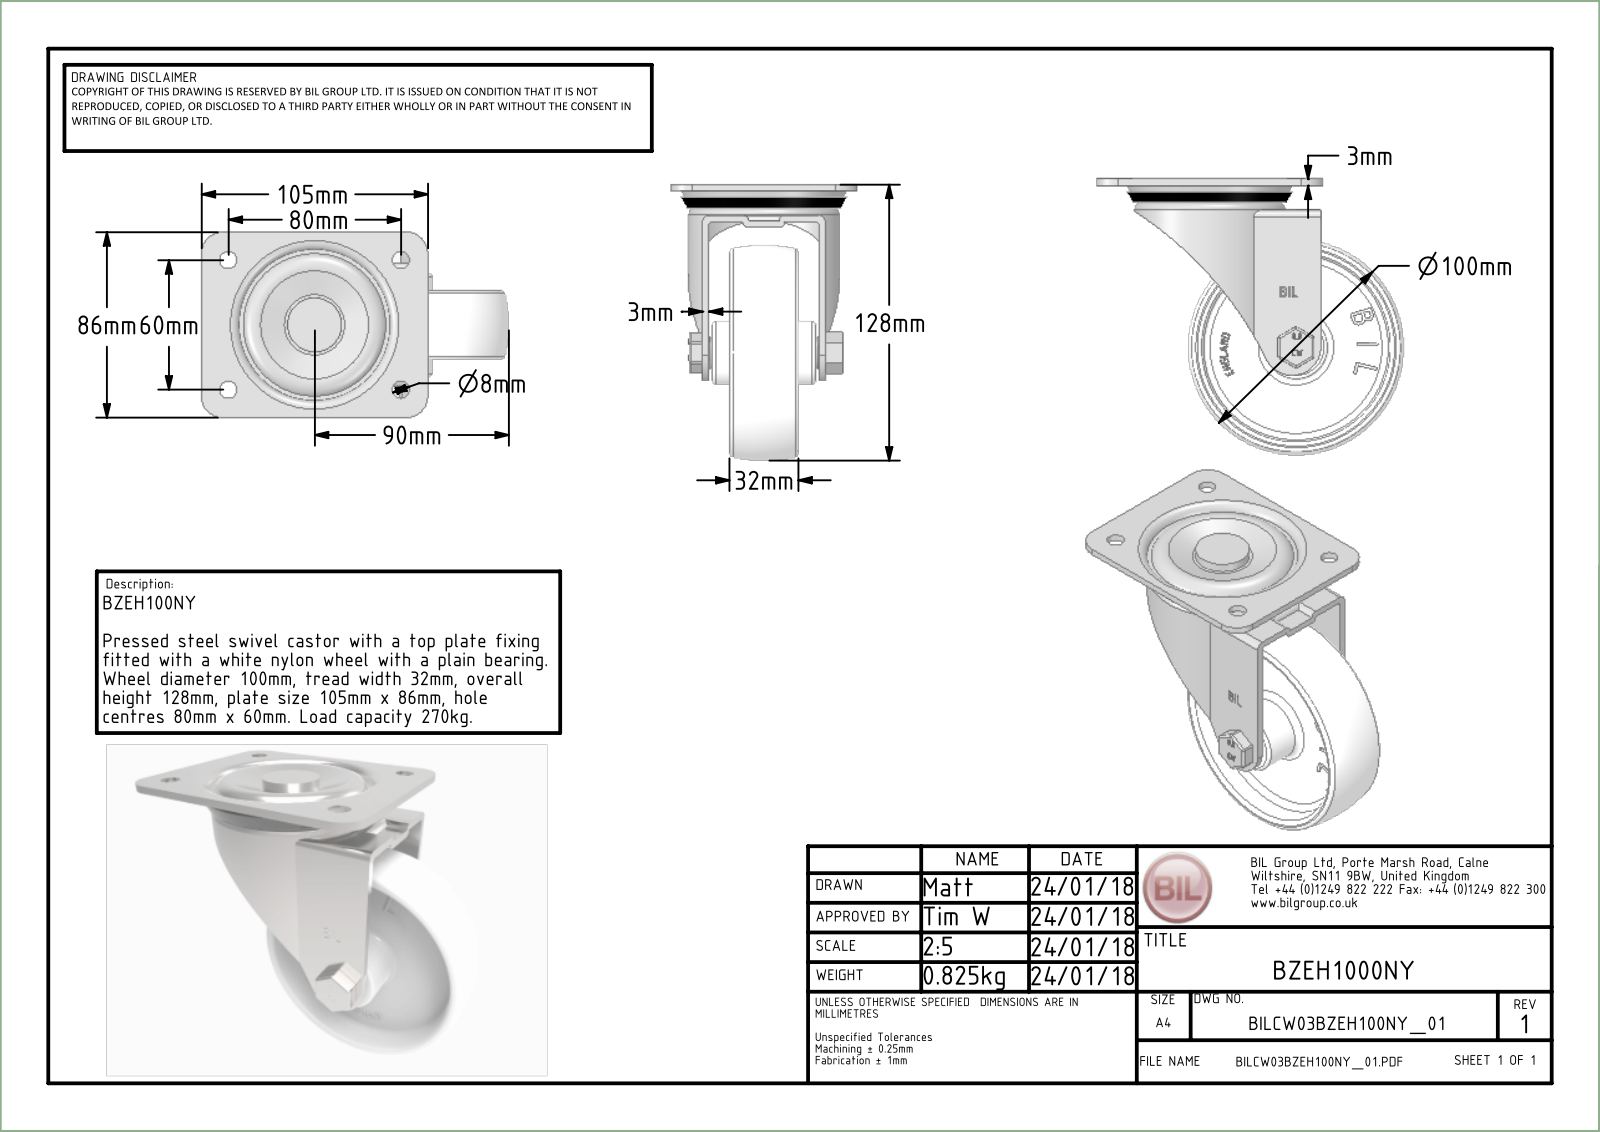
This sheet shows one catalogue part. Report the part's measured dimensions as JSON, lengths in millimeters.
{"part_name": "BZEH100NY v3; BZEH100AS - 2 v2; ZINC PLATED, PRESSED STEEL TOP PLATE; ZINC PLATED, PRESSED STEEL TOP PLATE Geometry (+7 more)", "step_written_by": "Autodesk Translation Framework v14.4.0.0 (AUTOMOTIVE_DESIGN)", "units": "millimeters", "bodies": {"solids": 28, "faces": 632, "planar": 329, "cylindrical": 109, "other": 194}, "overall_size": [142.5, 128, 86], "volume_mm3": 218162, "surface_area_mm2": 103262, "round_holes": [[10, 1], [10.2, 1], [10.5, 1], [12, 1], [15, 1], [30, 1], [64, 1]], "round_bosses_or_shafts": [[70, 1], [54, 1], [25, 1], [21, 1], [16, 1], [9.85, 1], [8.14, 1]], "partial_cylinders_radius": [[0.5, 18], [4.5, 8], [0.75, 6], [10, 4], [1.25, 3], [3, 2], [24.04, 2], [14.1, 1]], "face_to_face_distances": [3, 5, 10, 6, 2, 8, 31.5, 25.5, 7, 28.5]}
